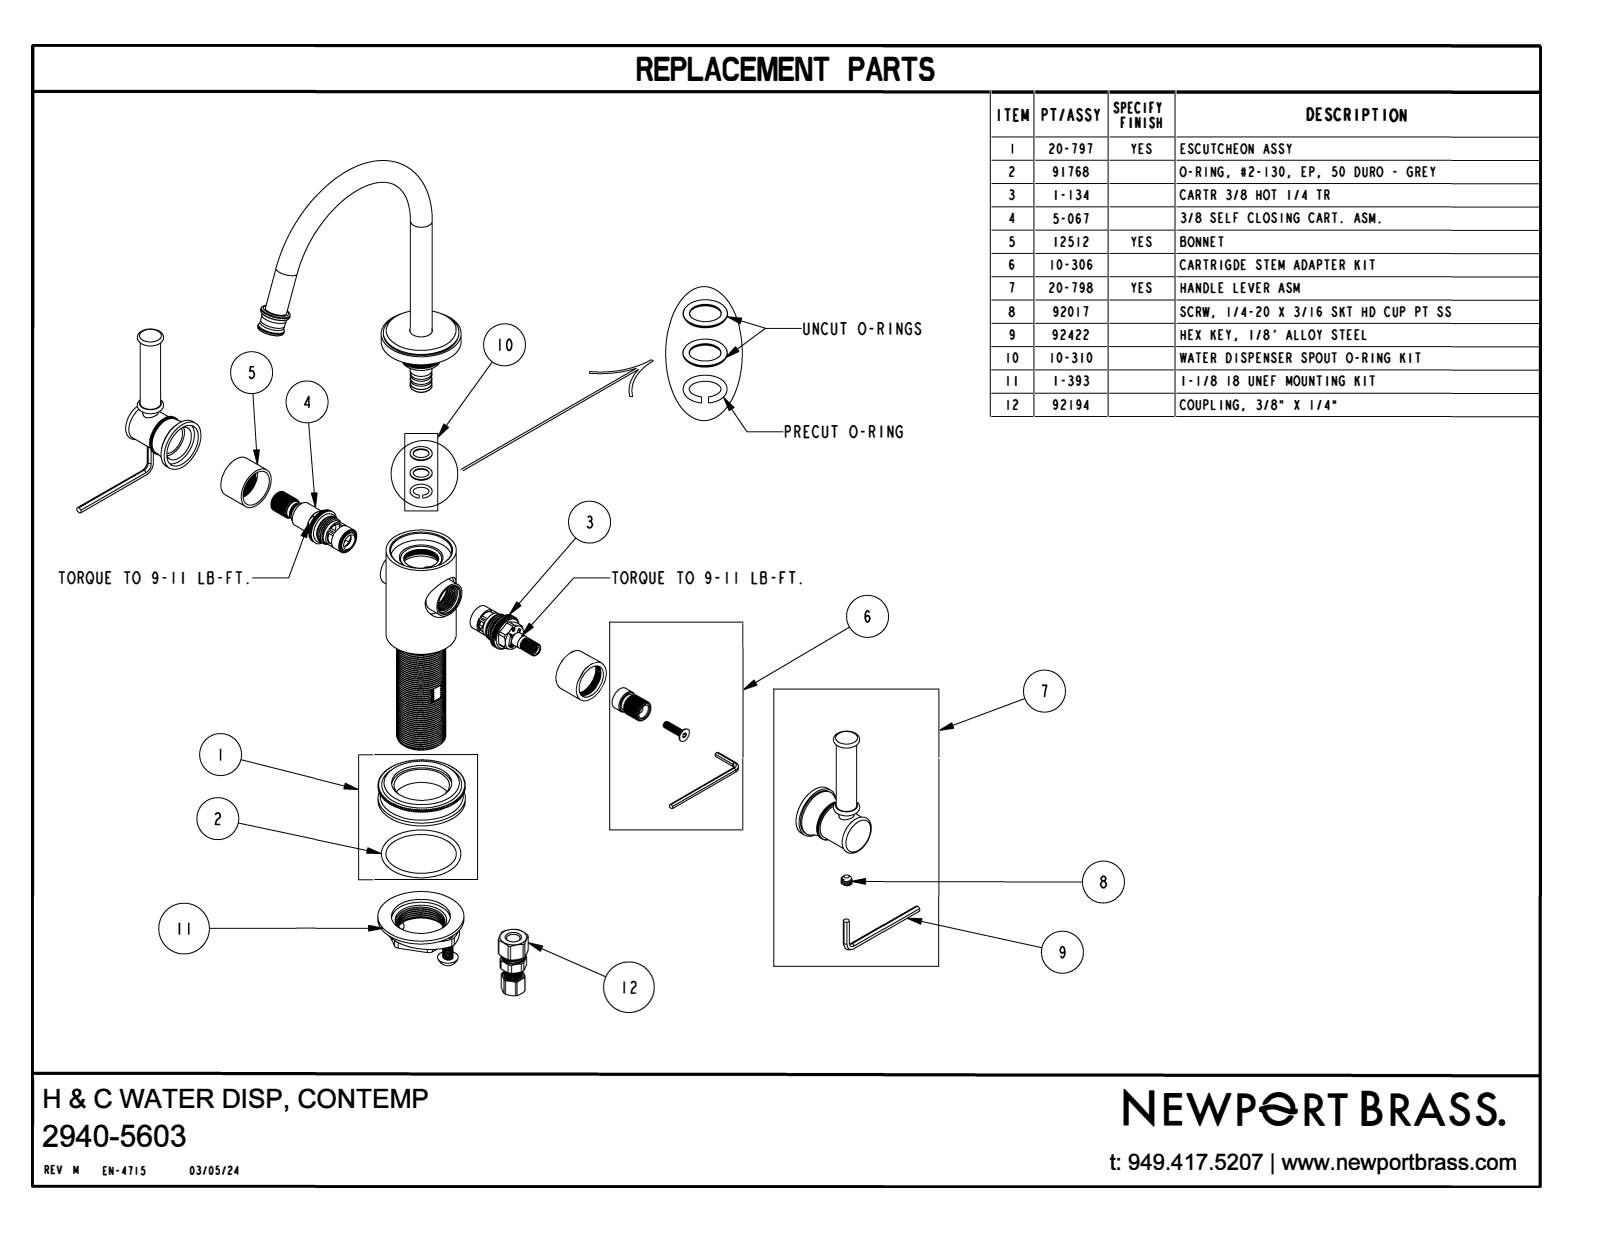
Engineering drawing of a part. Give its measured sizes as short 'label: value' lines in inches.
name: 2940-5603
written by: CREO PARAMETRIC BY PTC INC, 2018400 (CONFIG_CONTROL_DESIGN)
unit: in
bodies: 1 solid, 938 faces (568 planar, 316 cylindrical, 54 other)
size: 9.572 × 6.028 × 5.15
volume: 12.59 in³; area: 64.07 in²
holes: 1× ⌀1
bosses: 2× ⌀0.5, 2× ⌀0.468, 2× ⌀0.342, 2× ⌀0.335, 1× ⌀2, 1× ⌀1.904, 1× ⌀1.83, 1× ⌀1.73
rounds: 2× R0.179, 1× R0.47
face distances: 3.225, 1.42, 3.73, 0.5, 5.15, 0.445, 2.78, 4.524, 4.079, 1.299
